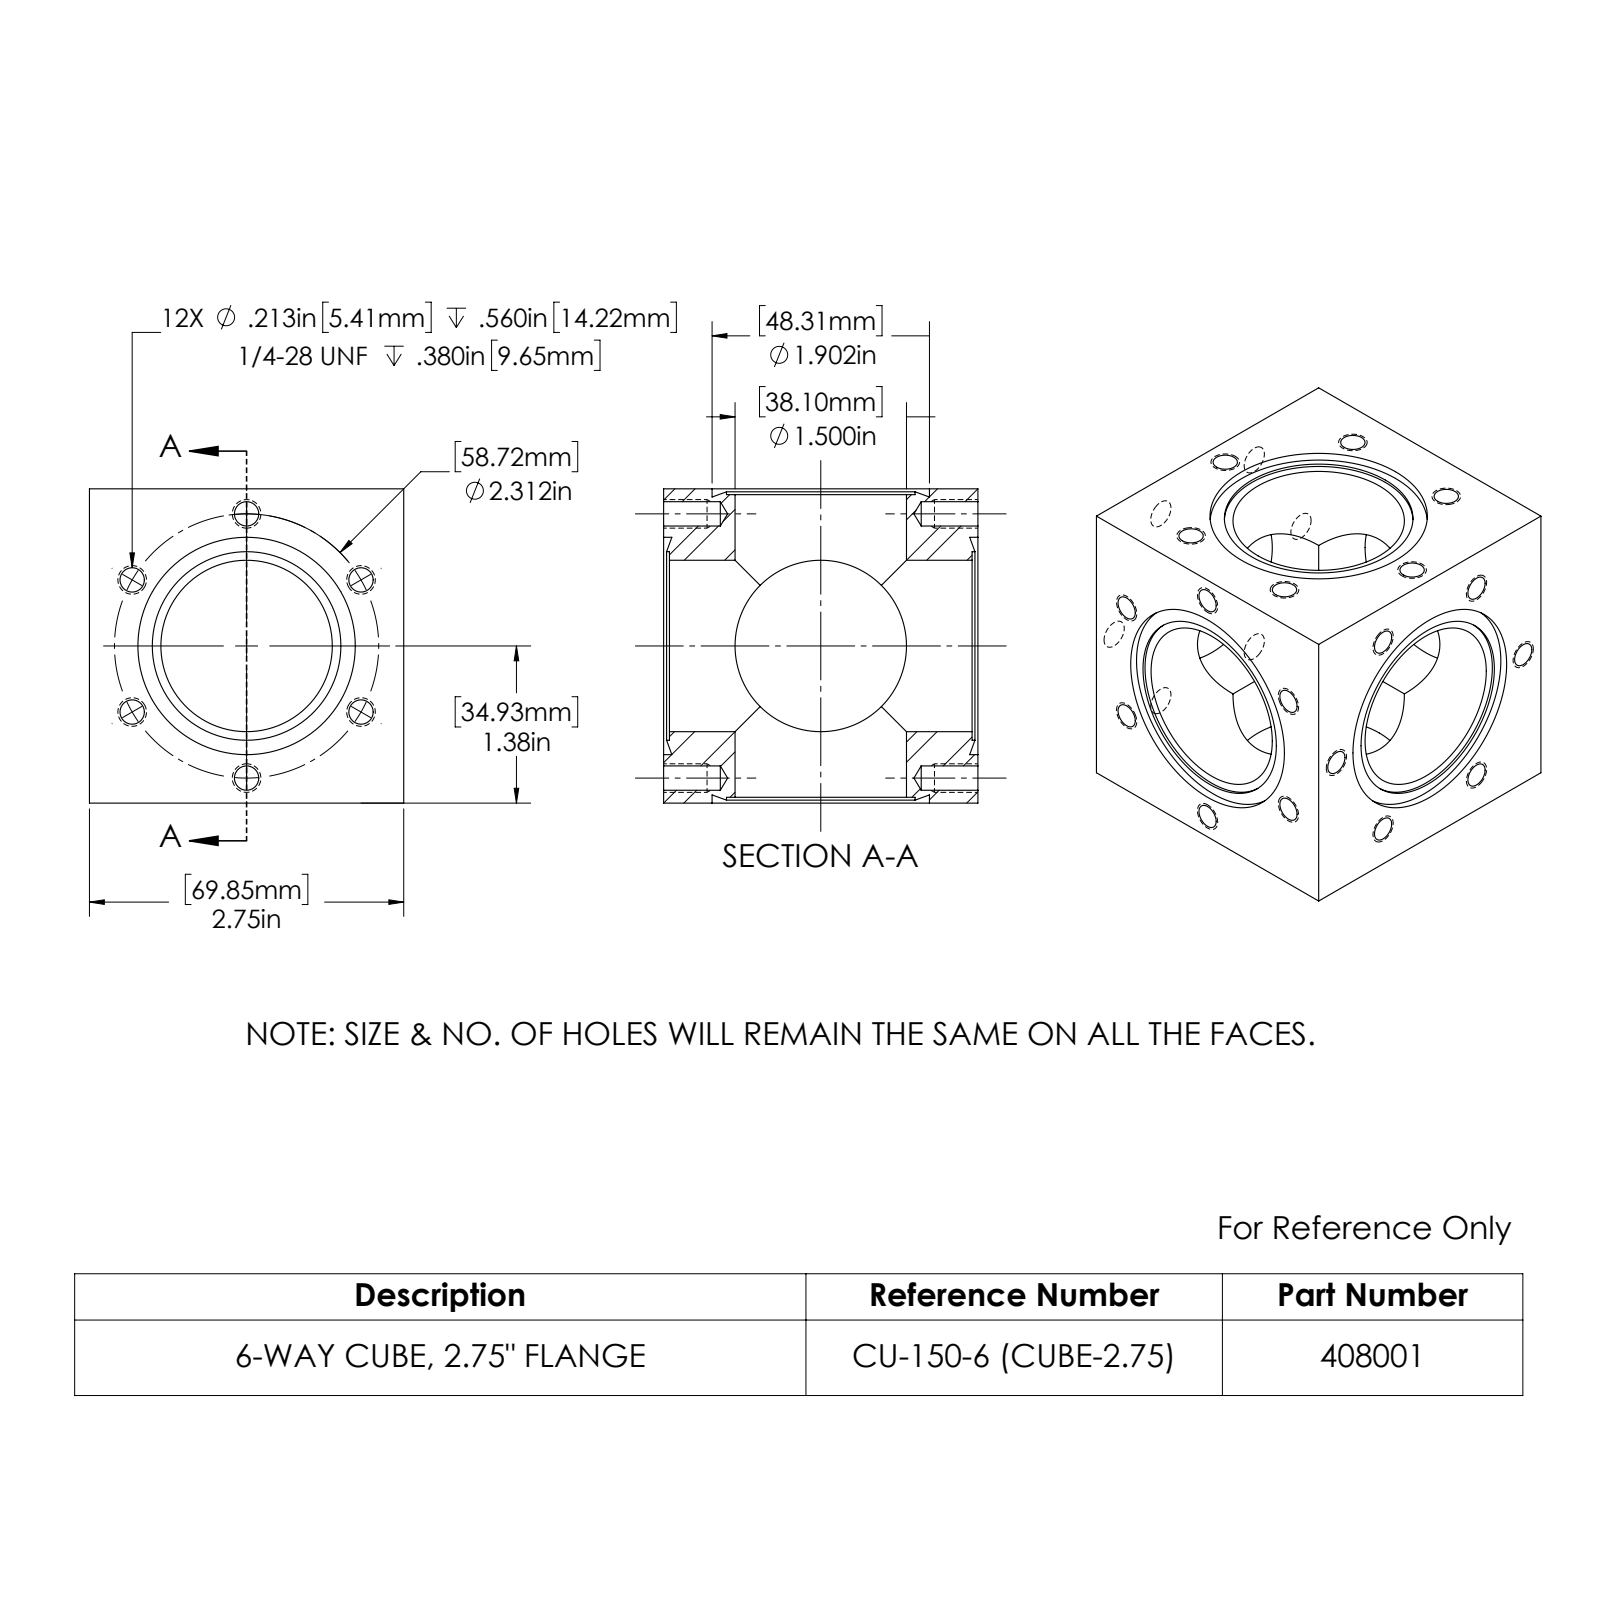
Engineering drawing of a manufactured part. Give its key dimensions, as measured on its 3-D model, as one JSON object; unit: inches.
{"part_name": "408001", "step_written_by": "SolidWorks 2022 (AUTOMOTIVE_DESIGN)", "units": "inches", "bodies": {"solids": 1, "faces": 204, "planar": 12, "cylindrical": 108, "other": 84}, "overall_size": [2.75, 2.75, 2.75], "volume_in3": 10.01, "surface_area_in2": 68.9, "round_holes": [[0.213, 18], [1.5, 3], [1.65, 3], [1.902, 3]], "face_to_face_distances": [2.75, 0.051, 2.699, 2.648], "hole_center_spacings": [1.156, 2.002, 2.002, 2.312, 2.312]}
